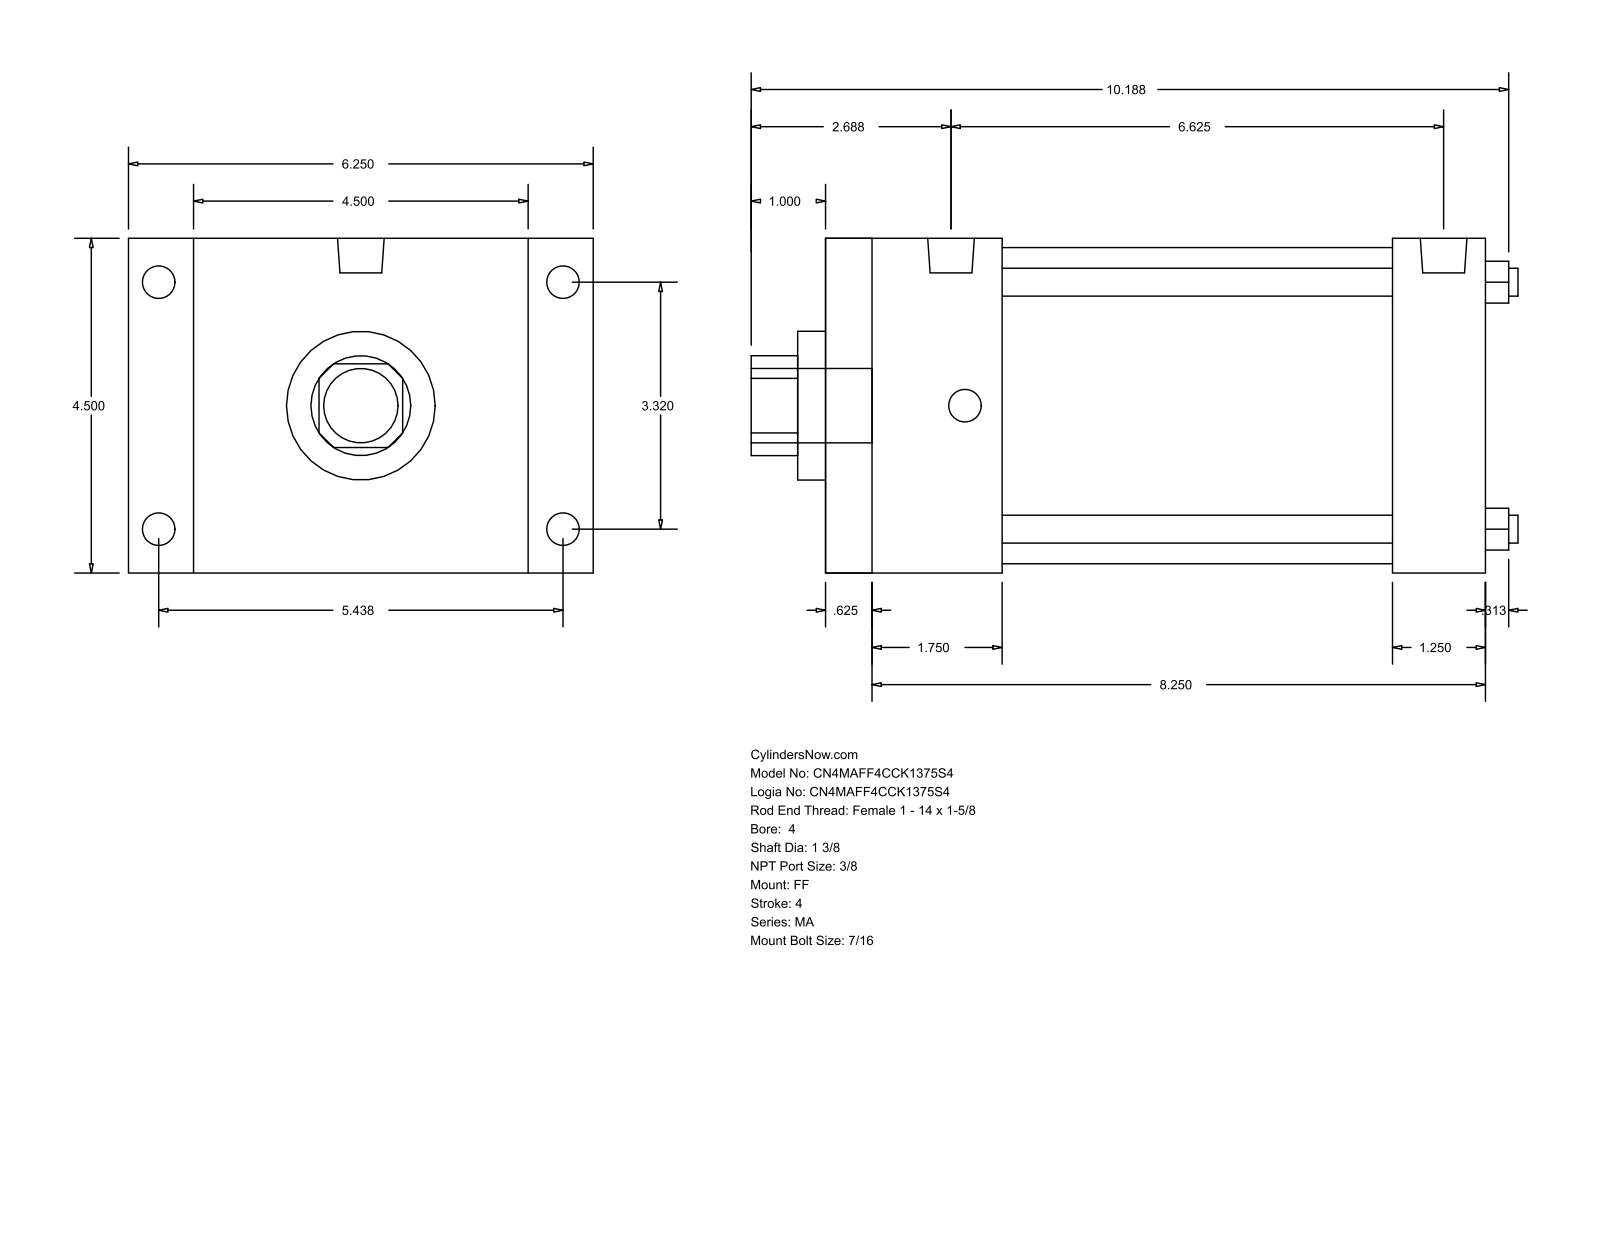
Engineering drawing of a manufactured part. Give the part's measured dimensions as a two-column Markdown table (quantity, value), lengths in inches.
| quantity | value |
| --- | --- |
| part name | MA_FF__0400_1.375 |
| STEP written by | GSSL Pune (CONFIG_CONTROL_DESIGN) |
| units | inches |
| bodies | 0 solids, 92 faces (64 planar, 28 cylindrical, 0 other) |
| overall size | 10.313 × 6.25 × 4.5 |
| round holes (diameter × count) | 0.375 × 4, 1.375 × 1, 2 × 1, 4.25 × 1 |
| round bosses / shafts (diameter × count) | 0.437 × 8, 0.627 × 2, 1 × 1 |
| partial cylindrical surfaces (radius × count) | 0.672 × 1 |
| main face-to-face distances | 4.5, 8.875, 0.625, 8.25, 0.875, 5.375, 7.625, 7, 1.25, 2.375 |
| hole center spacings | 2.347, 3.32, 4.695 |
